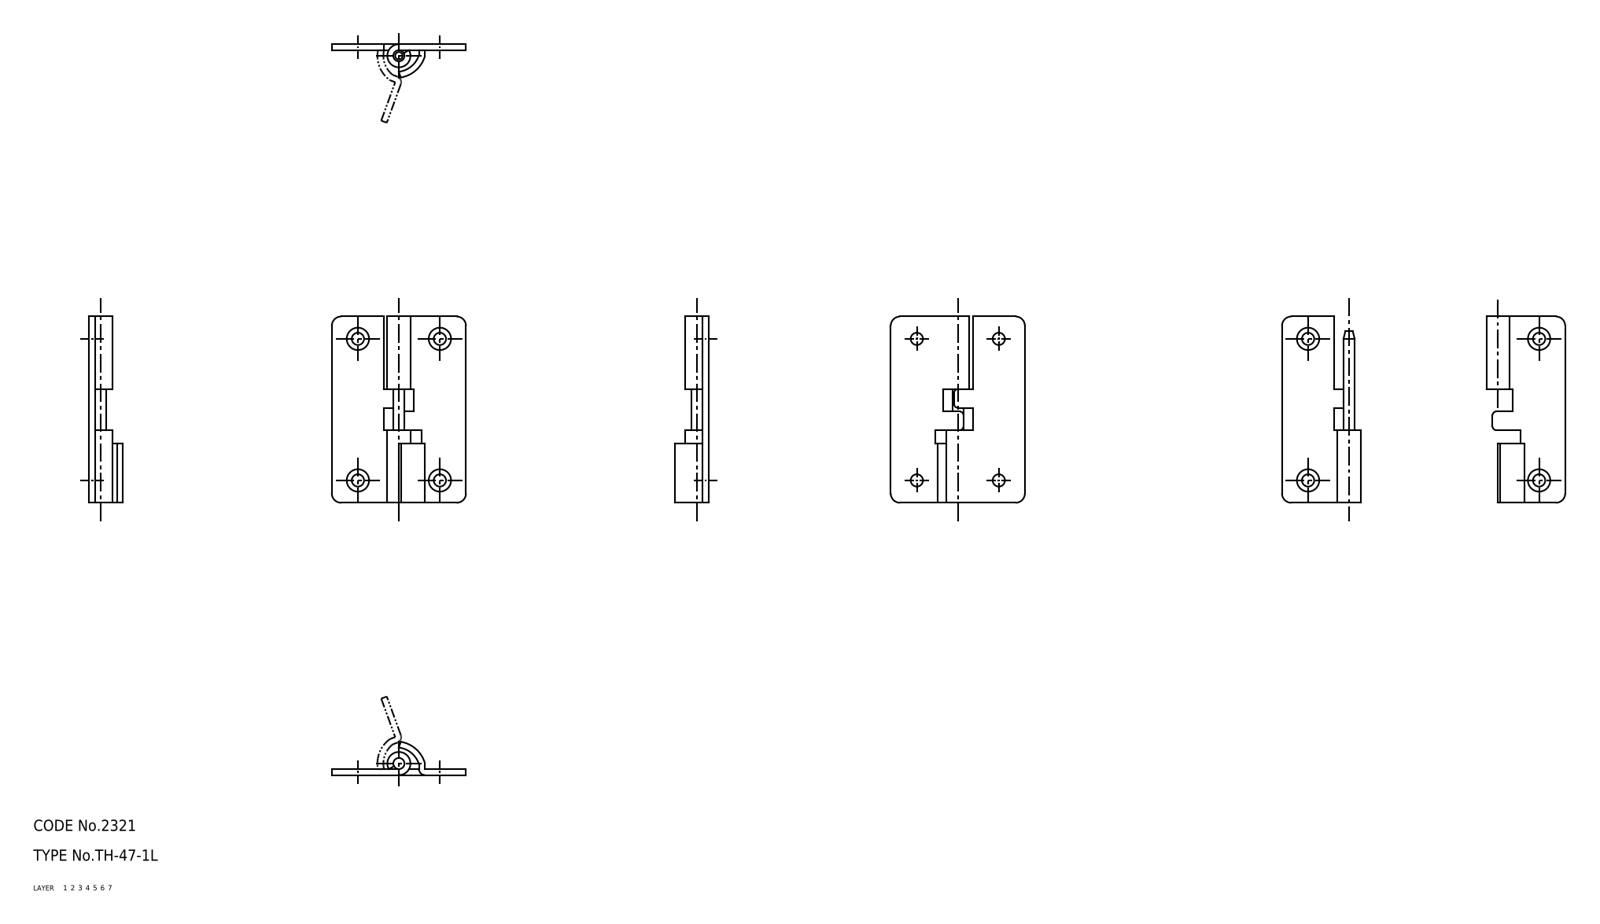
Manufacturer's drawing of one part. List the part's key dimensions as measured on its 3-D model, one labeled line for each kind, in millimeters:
Part name (STEP PRODUCT): shaft; hinge piece_B; hinge piece_A; TH_47_1L_9764_36
STEP written by: CADfix (AUTOMOTIVE_DESIGN)
Units: millimetres
Bodies: 3 solids, 65 faces (0 planar, 0 cylindrical, 65 other)
Overall size (bounding box): 50 × 36 × 9
Volume: 3 711 mm³ · Surface area: 5 349 mm²
